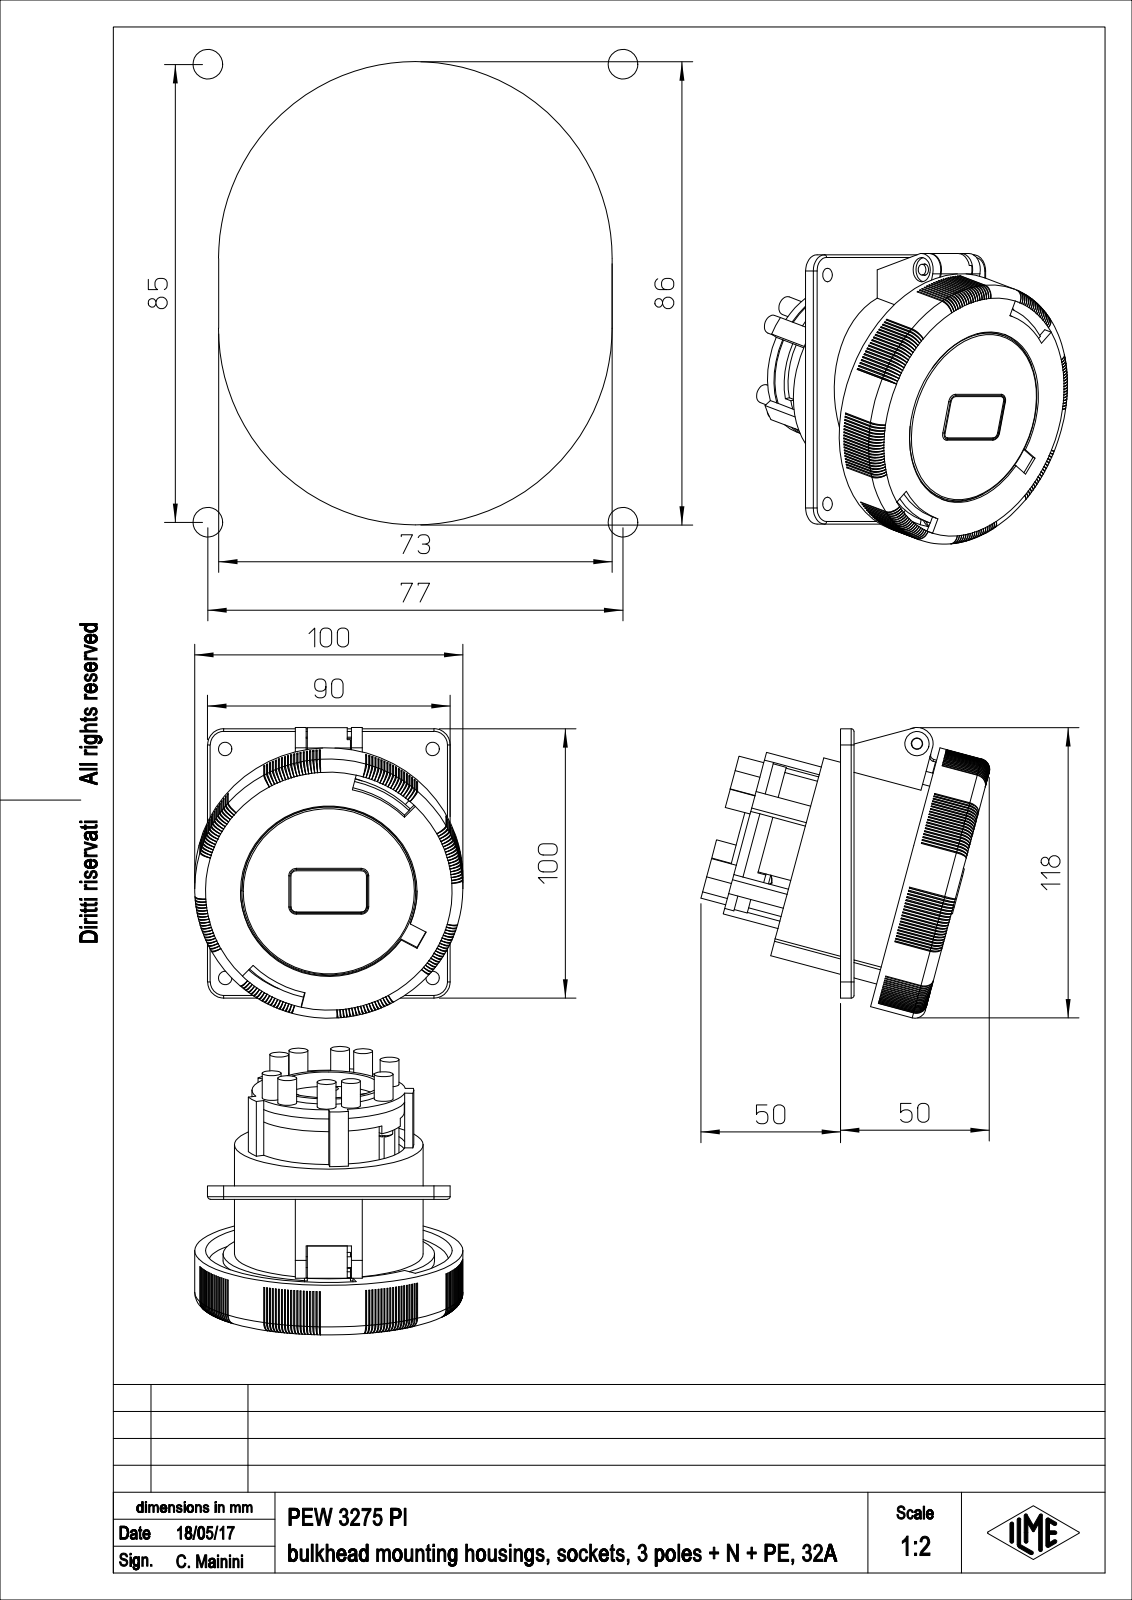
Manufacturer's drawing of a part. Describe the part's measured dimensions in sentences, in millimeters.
The part is named "PEW_3275_PI". Its 3-D file was written by "PTC Creo Elements/Direct Modeling 19.0E 27-Jun-2016 (C) Parametric Technology GmbH (AUTOMOTIVE_DESIGN)". It is 1 solid with 1440 faces: 642 planar, 307 cylindrical and 491 other. Overall it measures 107.91 by 107.09 by 99.5 millimeters. Its volume is 269 783 cubic millimeters and its surface area 105 069 square millimeters. Round holes: 5 of diameter 7, 4 of diameter 5, 4 of diameter 7.5, 4 of diameter 14, 1 of diameter 4.2, 1 of diameter 9, 1 of diameter 9.5, 1 of diameter 37, 1 of diameter 57, 1 of diameter 58.5, 1 of diameter 61.7, 1 of diameter 65.3. Round bosses or shafts: 11 of diameter 7, 2 of diameter 6.7, 1 of diameter 99.5, 1 of diameter 85, 1 of diameter 78.5, 1 of diameter 75.5, 1 of diameter 70, 1 of diameter 64.5. Partial cylindrical surfaces (rounded edges, fillets, slot ends): 152 of radius 3.6, 6 of radius 6, 4 of radius 0.4, 4 of radius 1, 4 of radius 2, 3 of radius 0.2, 2 of radius 4, 2 of radius 26. The main face-to-face distances are 5, 3, 57.7, 2, 20, 17, 60.7, 40.7, 6.7, 11.19. The hole center spacings are 28.81, 17.81, 15.15, 15.14, 15.16, 28.82, 17.8, 15.12.
